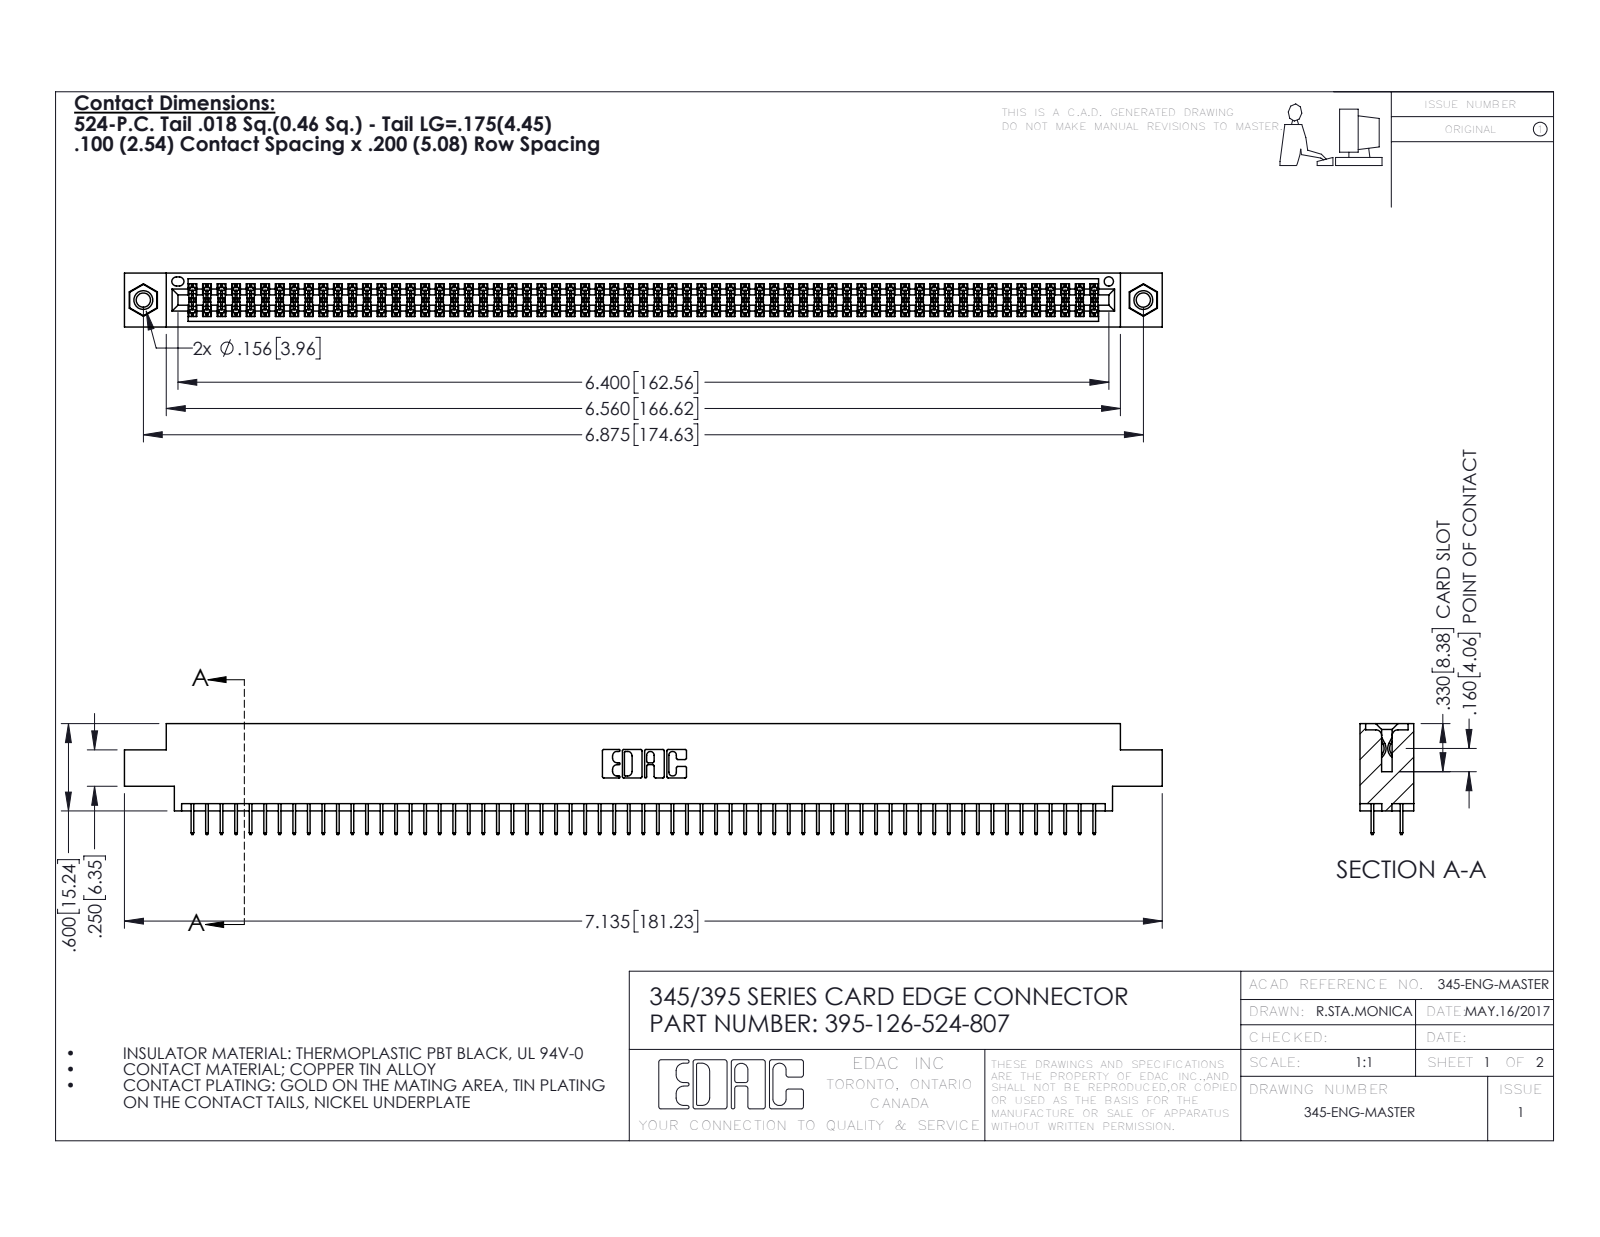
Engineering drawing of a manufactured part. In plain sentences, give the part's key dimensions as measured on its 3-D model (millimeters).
The part is named "395-126-524-807; 345-292-001_345-293-124; 345-250-001_345-250-005-103; 345 Part_0.170 Offset - 0.156 Dia-TI". Its 3-D file was written by "SolidWorks 2016 (CONFIG_CONTROL_DESIGN)". It is 129 solids with 6994 faces: 5030 planar, 1948 cylindrical and 16 other. Overall it measures 181.2 by 19.4 by 9.4 millimeters. Its volume is 17 480 cubic millimeters and its surface area 25 920 square millimeters. Round holes: 2 of diameter 2.5, 2 of diameter 3.2, 2 of diameter 4, 1 of diameter 1.6. Round bosses or shafts: 2 of diameter 3.9. Partial cylindrical surfaces (rounded edges, fillets, slot ends): 189 of radius 0.2, 22 of radius 0.3, 6 of radius 0.2, 6 of radius 0.8, 3 of radius 0.7, 2 of radius 0.4, 2 of radius 0.5, 2 of radius 0.6. The main face-to-face distances are 1.8, 7.6, 5.1, 9.4, 2.5, 6.9, 0.6, 5.7, 1.8, 4.4. The hole center spacings are 6.9, 168.6, 174.6.
